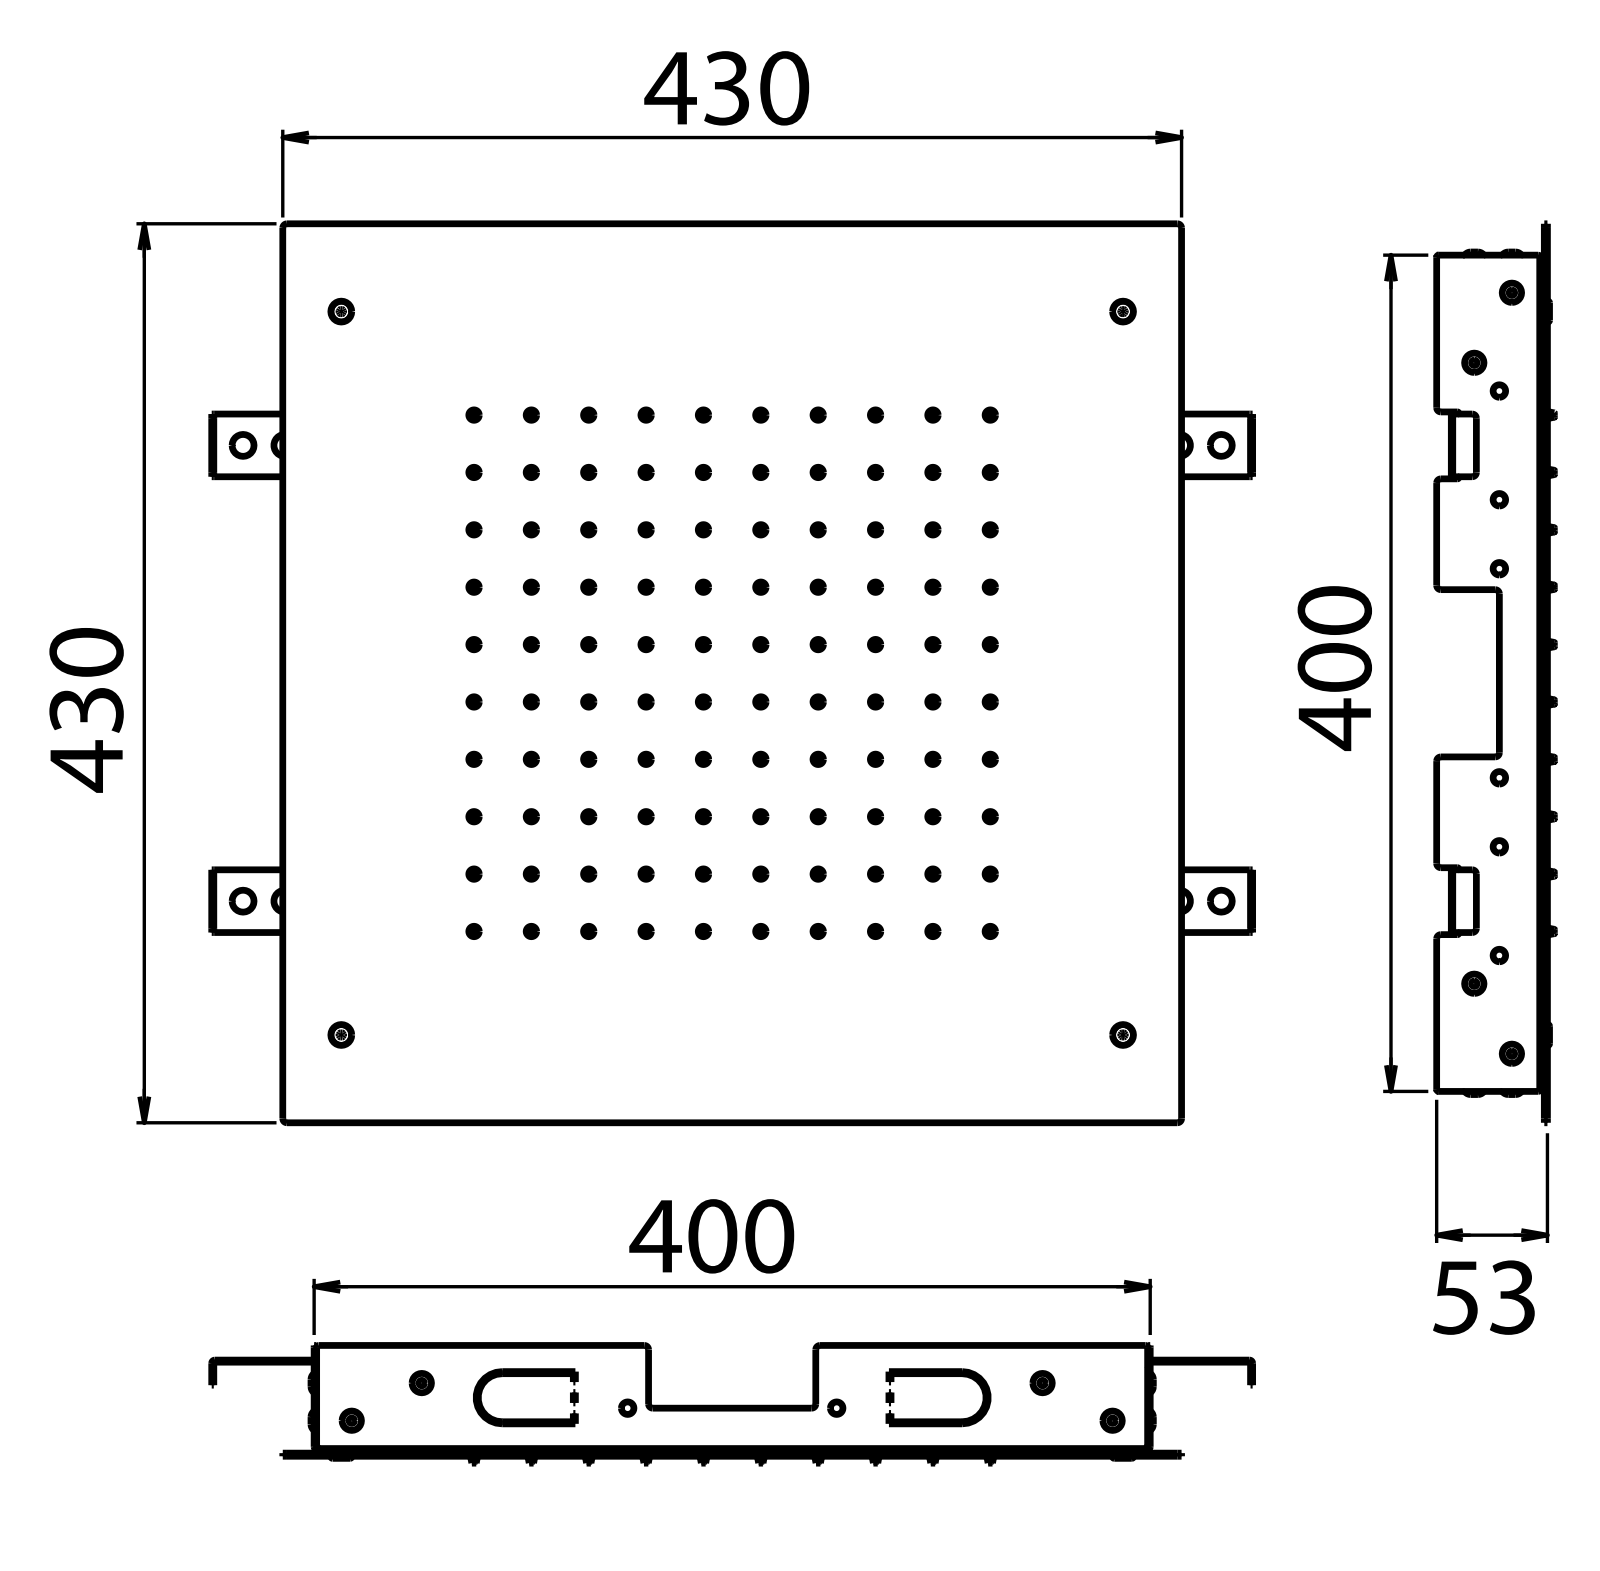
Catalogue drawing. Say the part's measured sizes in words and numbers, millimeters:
The part is named "A.R._24565/20220905". Its 3-D file was written by "Spatial InterOp 3D (AUTOMOTIVE_DESIGN)". It is 1 solid with 3380 faces: 1063 planar, 1054 cylindrical and 1263 other. Overall it measures 498 by 430 by 56.3 millimeters. Its volume is 688 269 cubic millimeters and its surface area 820 519 square millimeters. Round holes: 104 of diameter 5, 100 of diameter 1.5, 100 of diameter 1.7, 12 of diameter 5.2, 12 of diameter 6.2, 8 of diameter 2.6, 8 of diameter 4.4, 8 of diameter 6, 8 of diameter 6.6, 8 of diameter 10.2, 8 of diameter 10.5, 4 of diameter 4.2. Round bosses or shafts: 104 of diameter 10, 12 of diameter 4.6, 12 of diameter 4, 8 of diameter 12, 8 of diameter 9.8, 8 of diameter 8.2, 8 of diameter 6.9, 8 of diameter 6. Partial cylindrical surfaces (rounded edges, fillets, slot ends): 176 of radius 0.2, 84 of radius 2, 44 of radius 1, 24 of radius 0.5, 16 of radius 1.5, 12 of radius 3.1, 8 of radius 0.1, 4 of radius 14.5. The main face-to-face distances are 1, 2.5, 4, 3, 1.5, 5.5, 6.5, 0.5, 2, 399. The hole center spacings are 61.49, 99.15, 137.5, 27.5, 38.89, 86.96, 122.98, 113.39.
